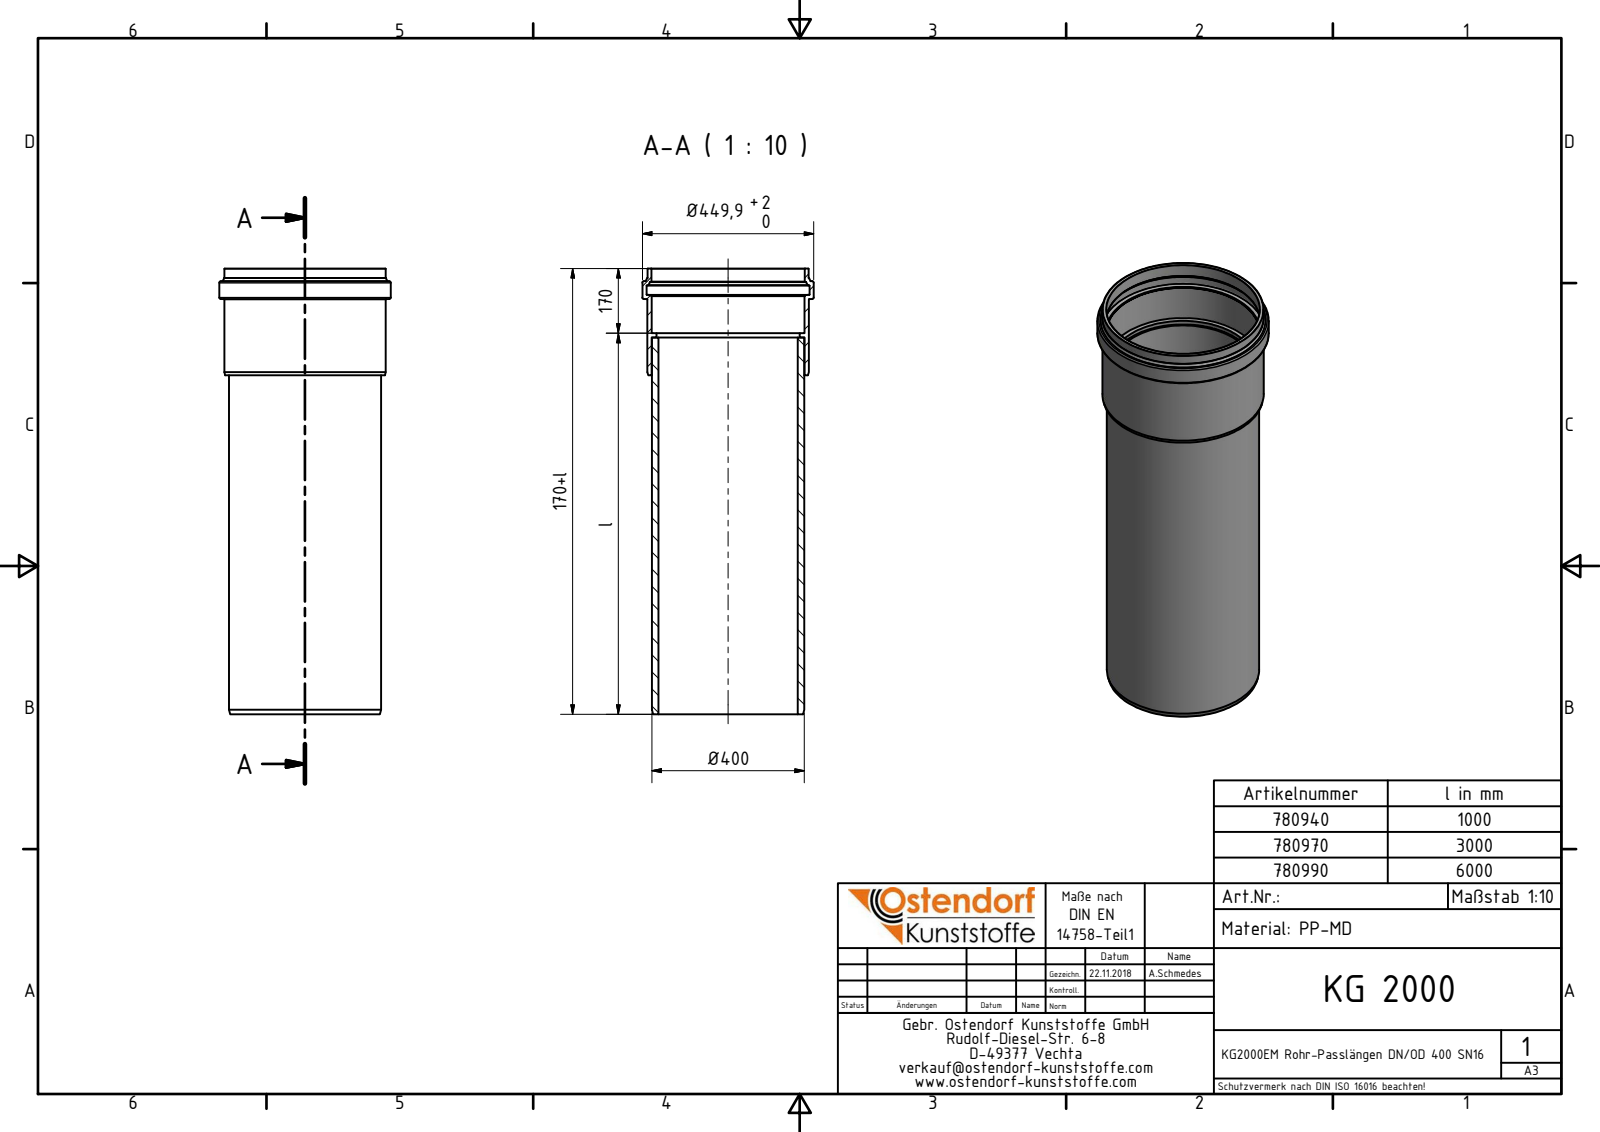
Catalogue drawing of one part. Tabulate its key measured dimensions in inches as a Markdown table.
| quantity | value |
| --- | --- |
| part name | 780970 KG2000EM Rohr-Passlängen DN_OD 400x3000 Teil 1 SN16; 780970 KG2000EM Rohr-Passlängen DN_OD 400x3000 Teil 2 SN16; 780970 KG2000EM Rohr-Passlängen DN_OD 400x3000 SN16 Zusammenbau |
| STEP written by | Autodesk Inventor 2016 (AUTOMOTIVE_DESIGN) |
| units | inches |
| bodies | 2 solids, 41 faces (9 planar, 11 cylindrical, 21 other) |
| overall size | 124.803 × 17.713 × 17.713 |
| volume | 4 026 in³ |
| surface area | 12 500 in² |
| round holes (diameter × count) | 14.402 × 1, 14.803 × 1, 15.815 × 1, 15.831 × 1, 16.839 × 1 |
| round bosses / shafts (diameter × count) | 17.713 × 1, 16.689 × 1, 16.656 × 1, 15.748 × 1 |
| main face-to-face distances | 117.673, 118.11, 0.437, 113.78, 3.894, 4.331, 124.803, 11.024, 7.13, 6.693 |
